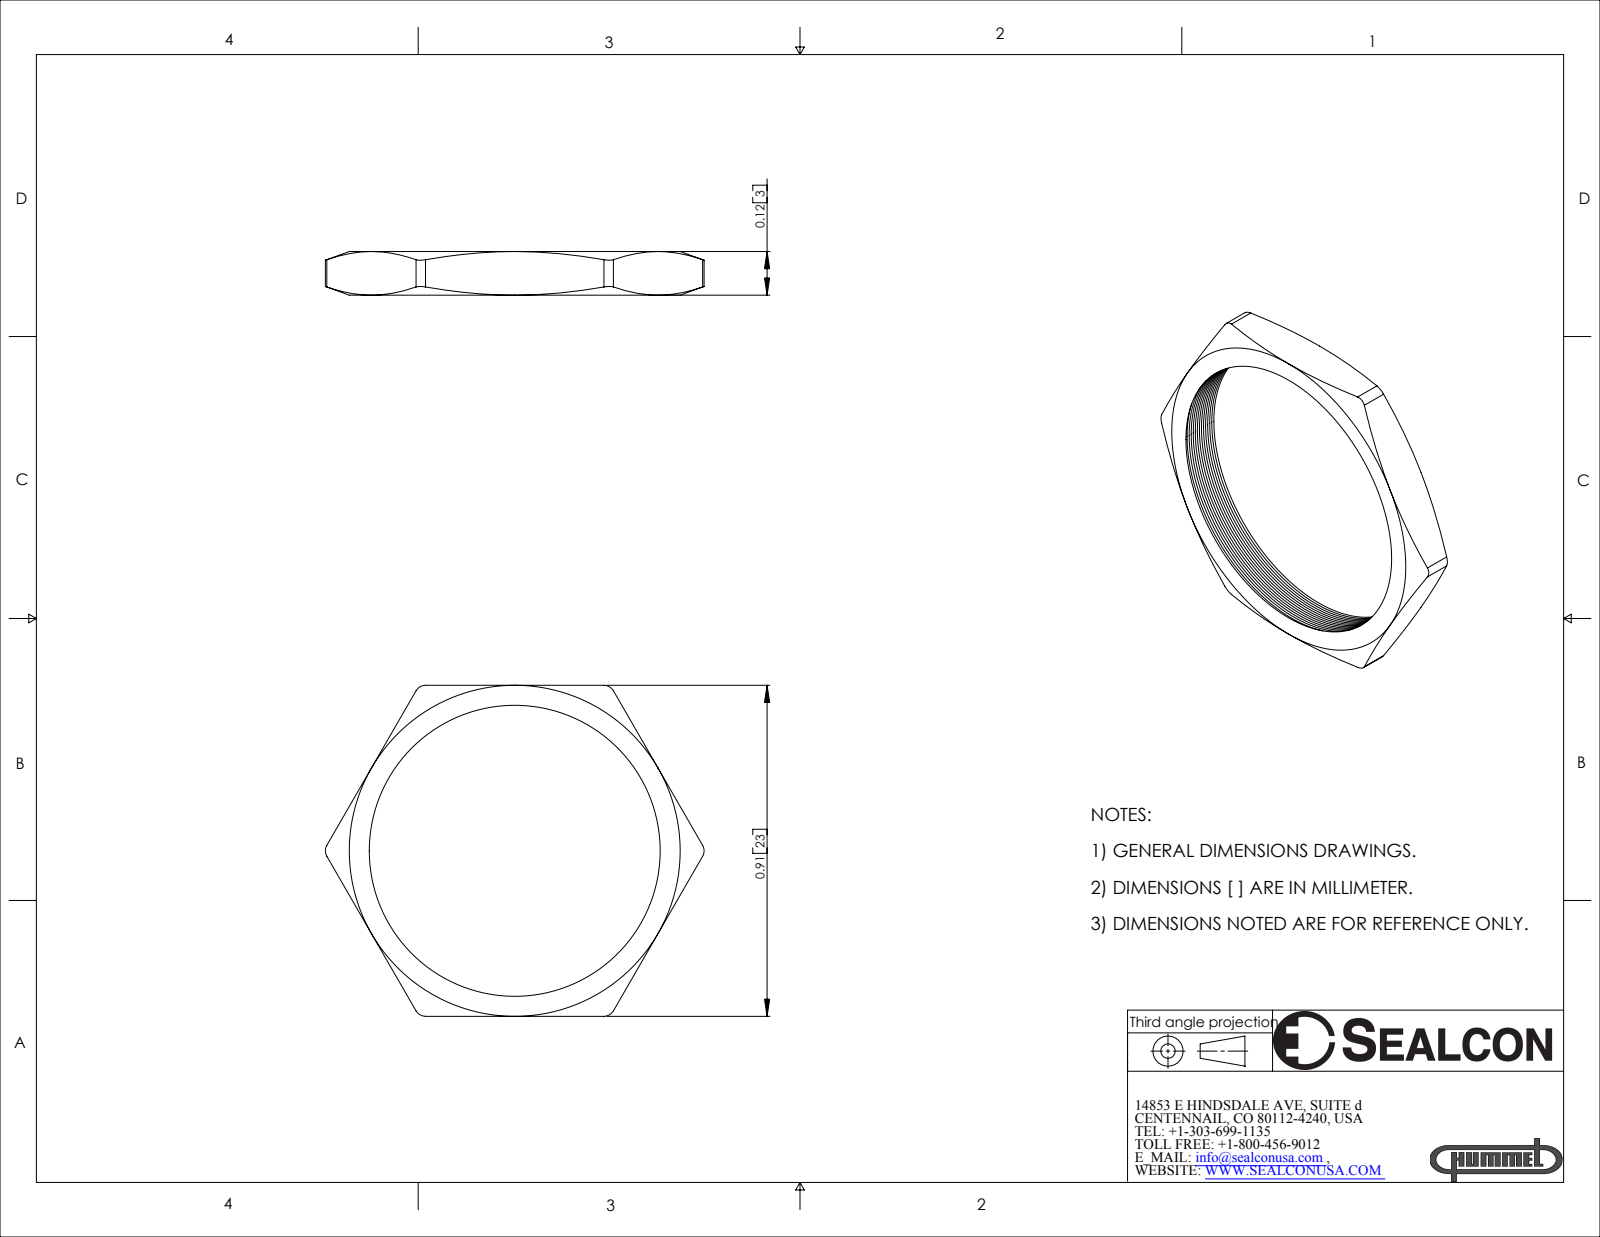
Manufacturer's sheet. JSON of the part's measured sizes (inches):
{"part_name": "NP-13-BR", "step_written_by": "SolidWorks 2007 (CONFIG_CONTROL_DESIGN)", "units": "inches", "bodies": {"solids": 1, "faces": 87, "planar": 8, "cylindrical": 7, "other": 72}, "overall_size": [1.041, 0.91, 0.12], "volume_in3": 0.021, "surface_area_in2": 1.343, "partial_cylinders_radius": [[0.03, 6]], "face_to_face_distances": [0.91, 0.12]}
